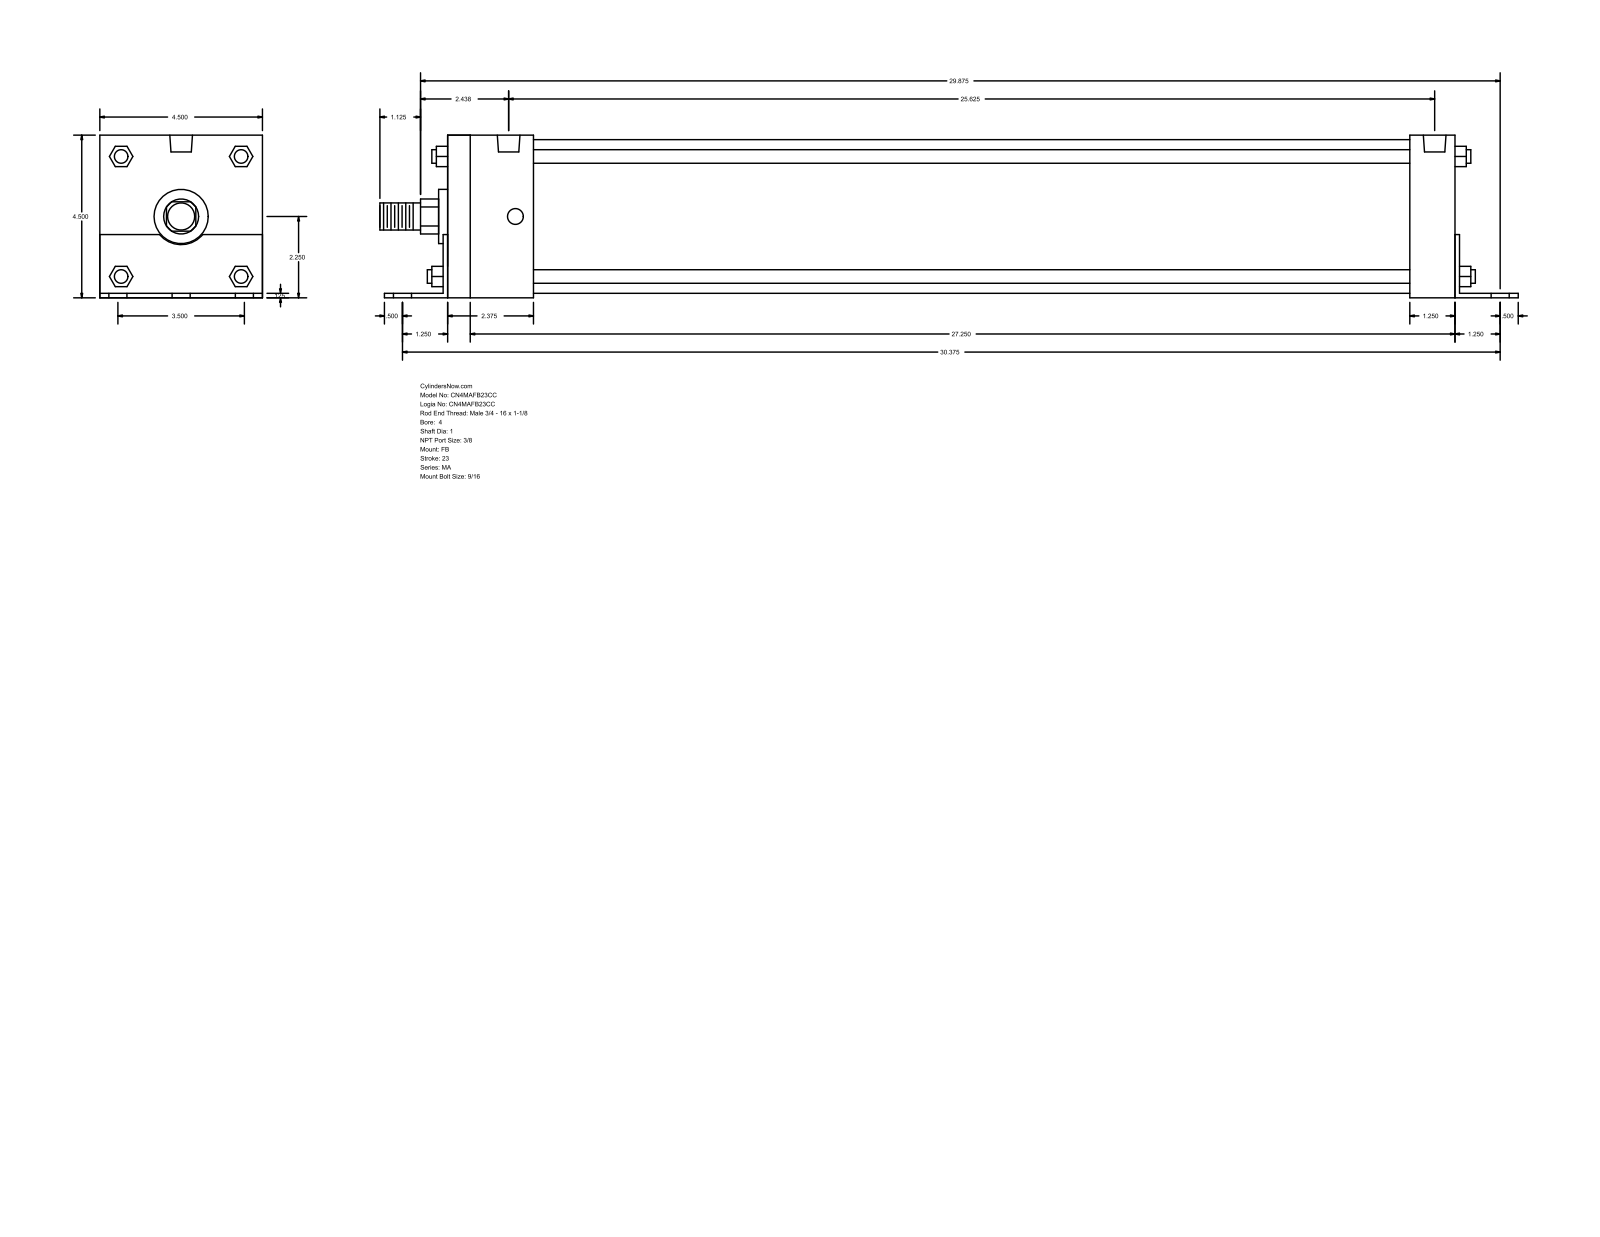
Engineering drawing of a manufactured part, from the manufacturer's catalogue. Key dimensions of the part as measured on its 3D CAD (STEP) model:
Part name (STEP PRODUCT): MA_FB__0400_1
STEP written by: GSSL Pune (CONFIG_CONTROL_DESIGN)
Units: millimetres
Bodies: 0 solids, 140 faces (105 planar, 35 cylindrical, 0 other)
Overall size (bounding box): 800.1 × 114.35 × 114.3
Round holes (diameter × count): ⌀14.29 ×6, ⌀11.11 ×4, ⌀15.93 ×2
Round bosses / shafts (diameter × count): ⌀9.53 ×4, ⌀107.95 ×1, ⌀38.1 ×1, ⌀25.4 ×1, ⌀19.05 ×1
Partial cylindrical surfaces — rounded edges, fillets, slot ends (radius × count): R12.29 ×1, R19.81 ×1
Main face-to-face distances: 114.3, 3.17, 114.35, 711.2, 3.12, 111.18, 708.03, 714.37, 679.45, 676.28
Hole centre spacings: 44.45, 772.81, 771.53, 64, 67.51, 86.85, 88.9, 90.97
